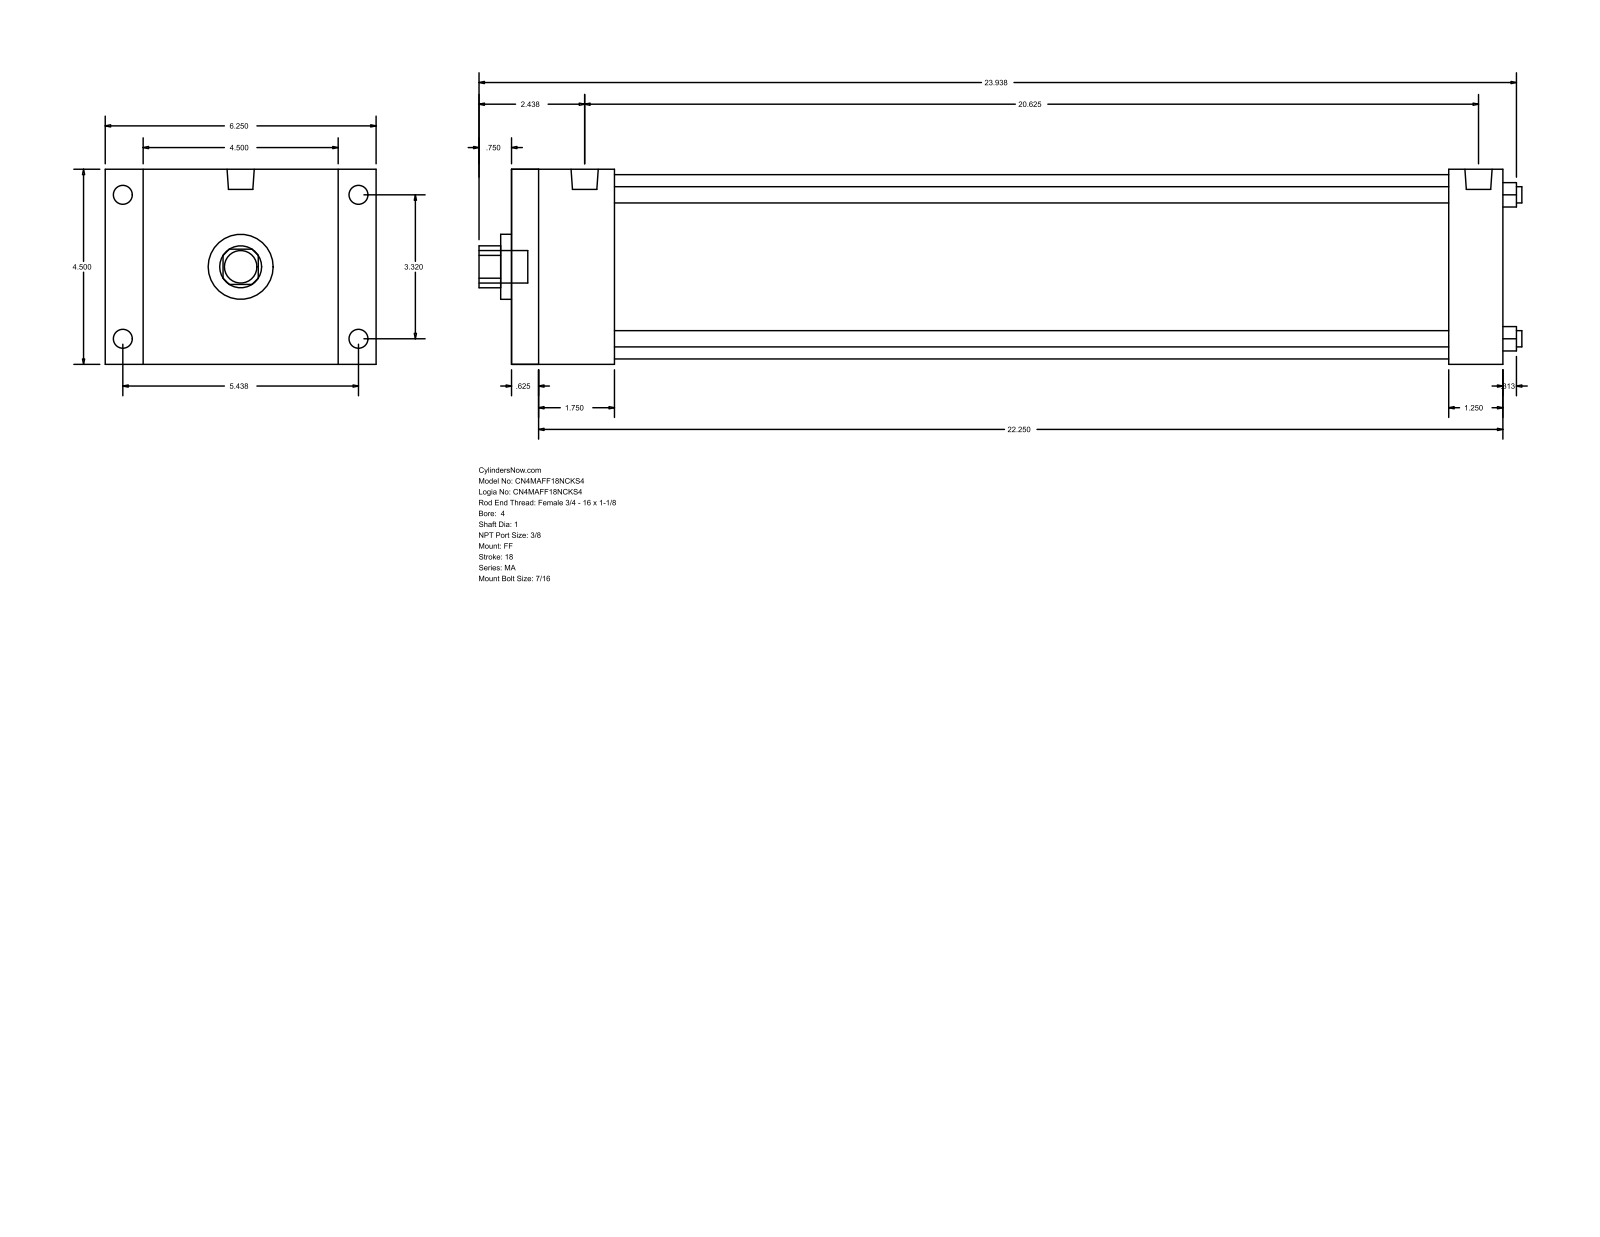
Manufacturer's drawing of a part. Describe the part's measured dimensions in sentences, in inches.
The part is named "MA_FF__0400_1". Its 3-D file was written by "GSSL Pune (CONFIG_CONTROL_DESIGN)". It is 0 solids with 92 faces: 64 planar, 28 cylindrical and 0 other. Overall it measures 24.063 by 6.25 by 4.5 inches. Round holes: 4 of diameter 0.375, 1 of diameter 1, 1 of diameter 1.5, 1 of diameter 4.25. Round bosses or shafts: 8 of diameter 0.437, 2 of diameter 0.627, 1 of diameter 0.75. Partial cylindrical surfaces (rounded edges, fillets, slot ends): 1 of radius 0.484. The main face-to-face distances are 4.5, 22.875, 0.625, 22.25, 0.875, 5.375, 21.625, 21, 1.25, 2.375. The hole center spacings are 2.347, 3.32, 4.695.
